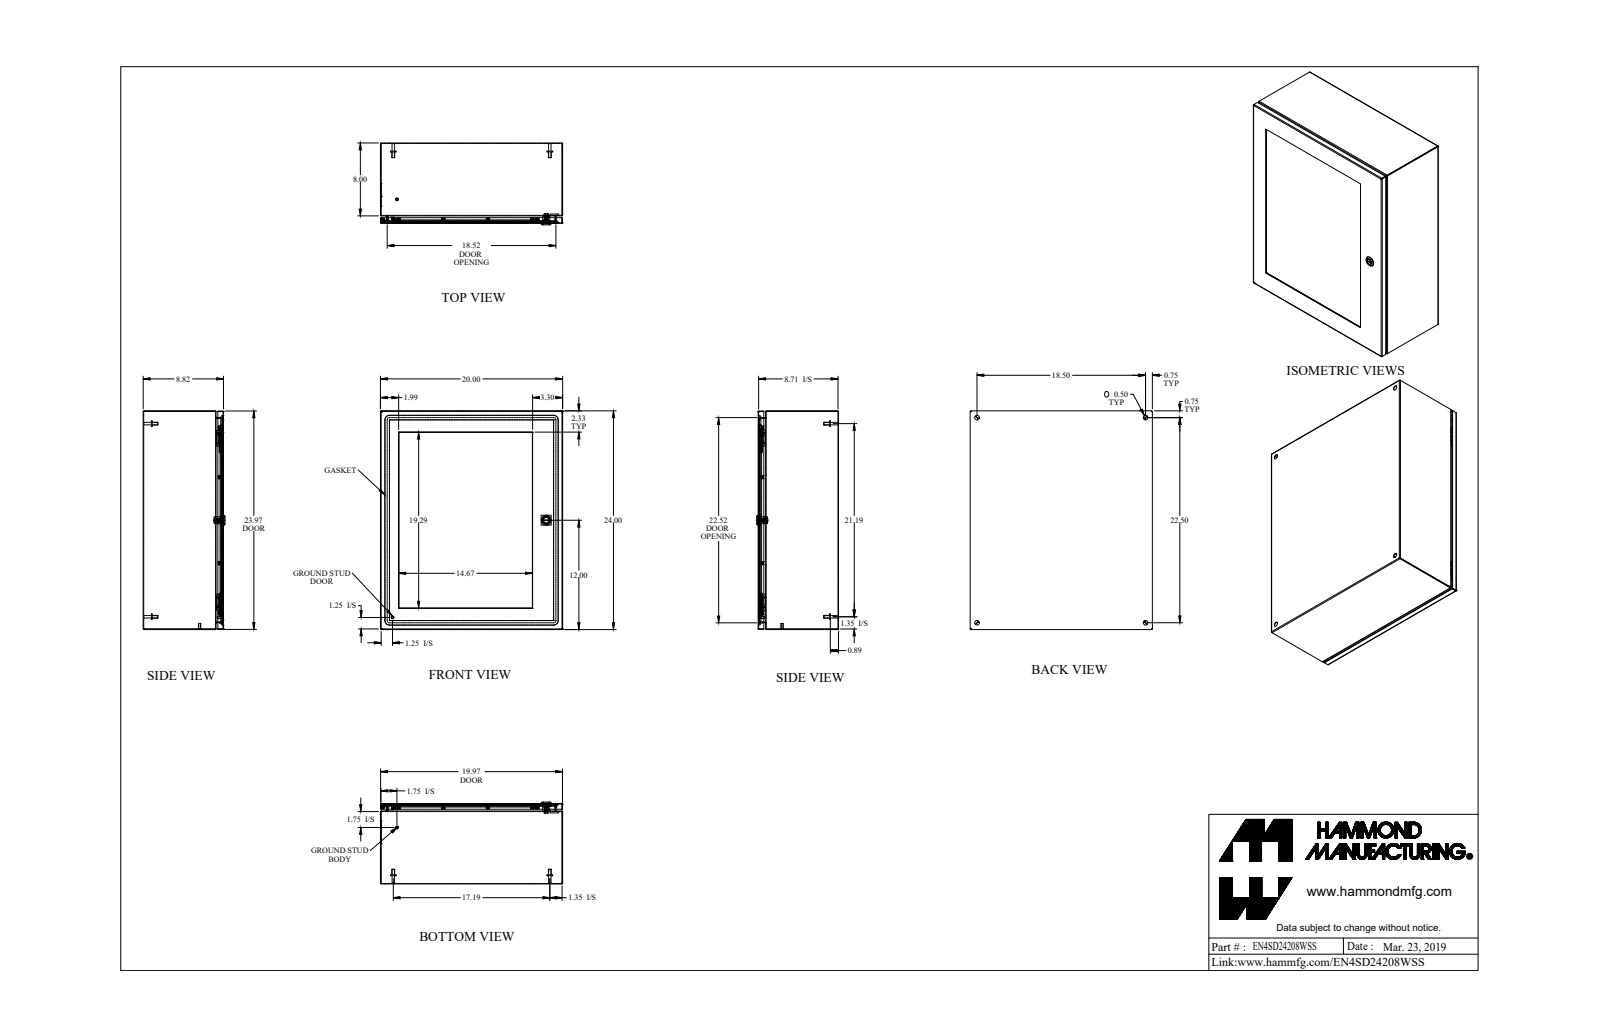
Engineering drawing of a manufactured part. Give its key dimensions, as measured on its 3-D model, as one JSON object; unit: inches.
{"part_name": "EN4SD24208WSS_Default", "step_written_by": "SolidWorks 2019 (CONFIG_CONTROL_DESIGN)", "units": "inches", "bodies": {"solids": 67, "faces": 1356, "planar": 680, "cylindrical": 408, "other": 268}, "overall_size": [24, 20, 8.982], "volume_in3": 178.9, "surface_area_in2": 4150, "round_holes": [[0.13, 18], [0.25, 18], [0.5, 5], [0.172, 1], [0.197, 1], [0.24, 1], [0.242, 1], [0.387, 1], [0.63, 1], [0.768, 1]], "round_bosses_or_shafts": [[0.226, 19], [0.368, 18], [0.164, 18], [0.313, 6], [0.625, 4], [0.275, 4], [0.25, 2], [1.1, 1]], "partial_cylinders_radius": [[0.029, 21], [0.086, 21], [0.188, 12], [0.125, 10], [0.006, 4], [0.016, 4], [0.062, 4], [0.088, 4]], "face_to_face_distances": [0.057, 8.765, 8.708, 19.943, 0.25, 8.458, 8.515, 23.943, 19.886, 20], "hole_center_spacings": [4.719, 4.89, 4.891, 9.78, 10.324, 16.401, 18.324, 20.333]}
